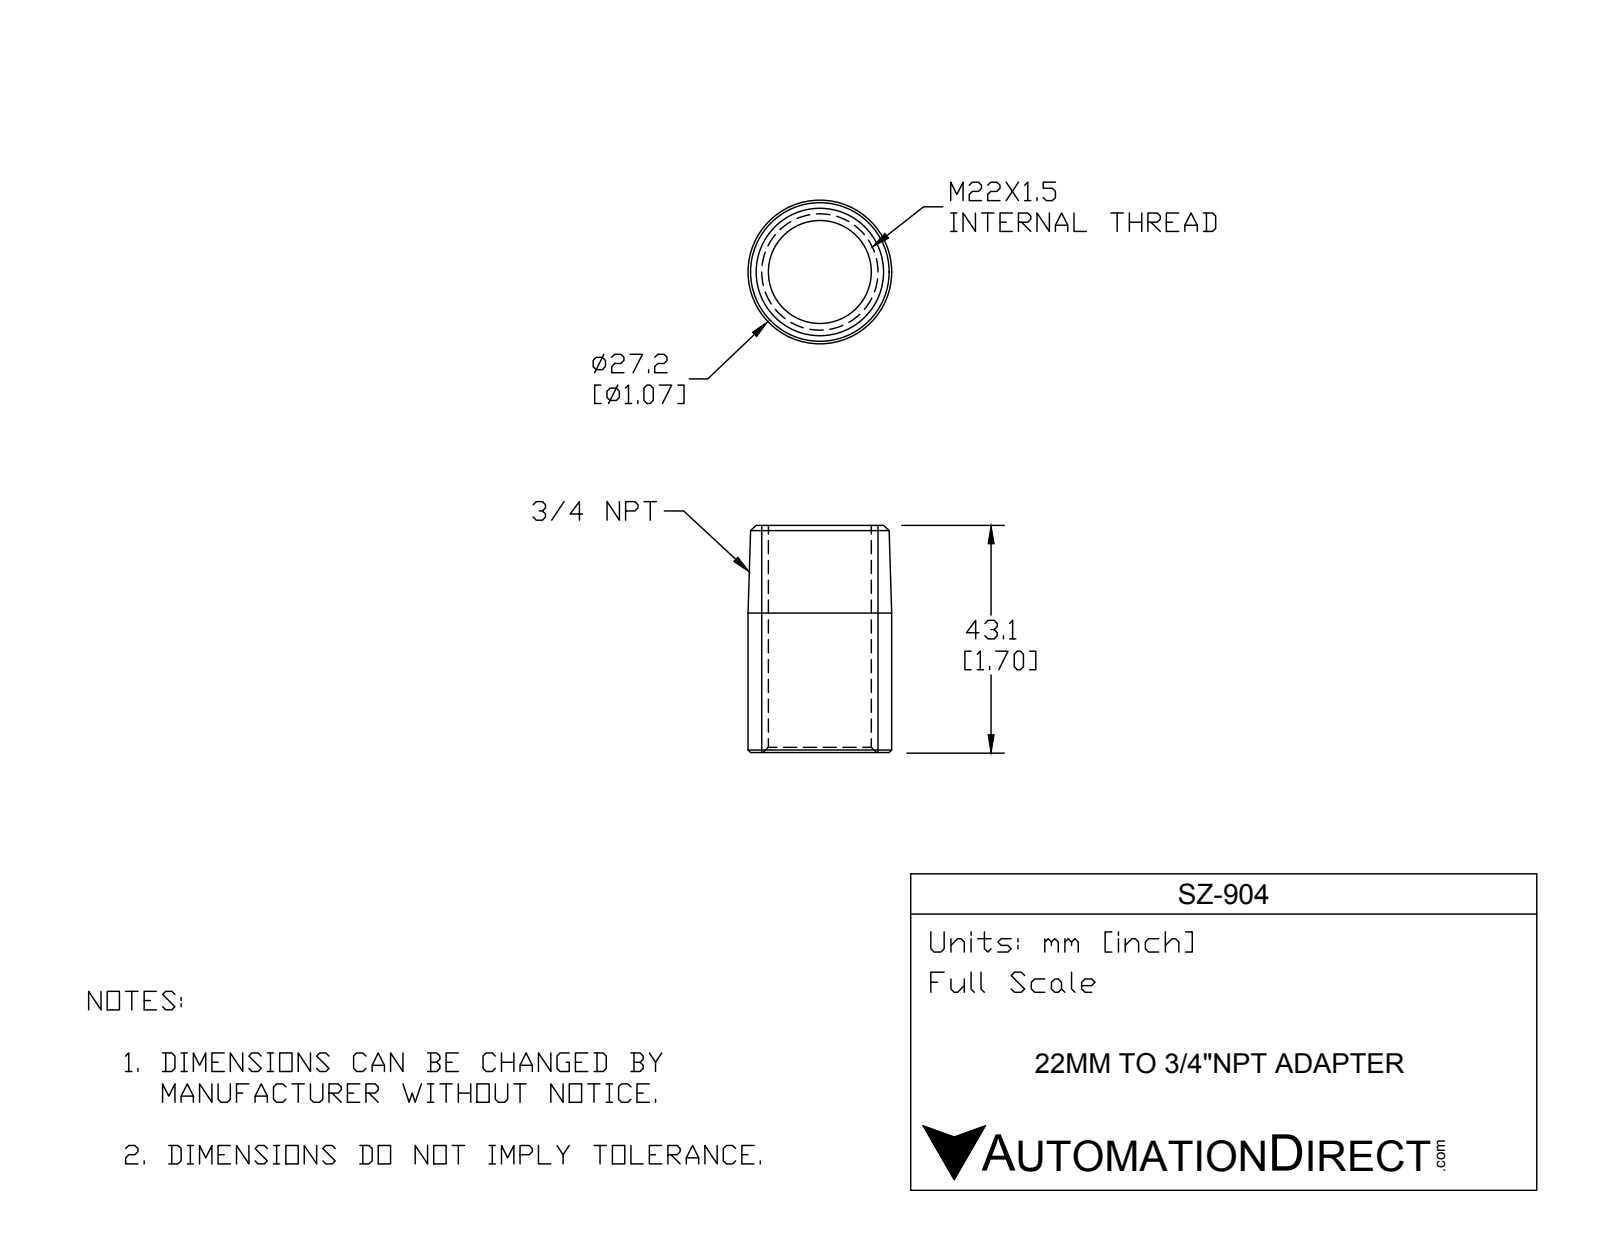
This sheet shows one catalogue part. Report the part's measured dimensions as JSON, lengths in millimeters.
{"part_name": "SZ-904", "step_written_by": "SolidWorks 2016 (AUTOMOTIVE_DESIGN)", "units": "millimeters", "bodies": {"solids": 1, "faces": 14, "planar": 2, "cylindrical": 4, "other": 8}, "overall_size": [43, 27.2, 27.2], "volume_mm3": 11701, "surface_area_mm2": 6696, "round_holes": [[19.5, 1]], "round_bosses_or_shafts": [[27.2, 1]], "face_to_face_distances": [43]}
